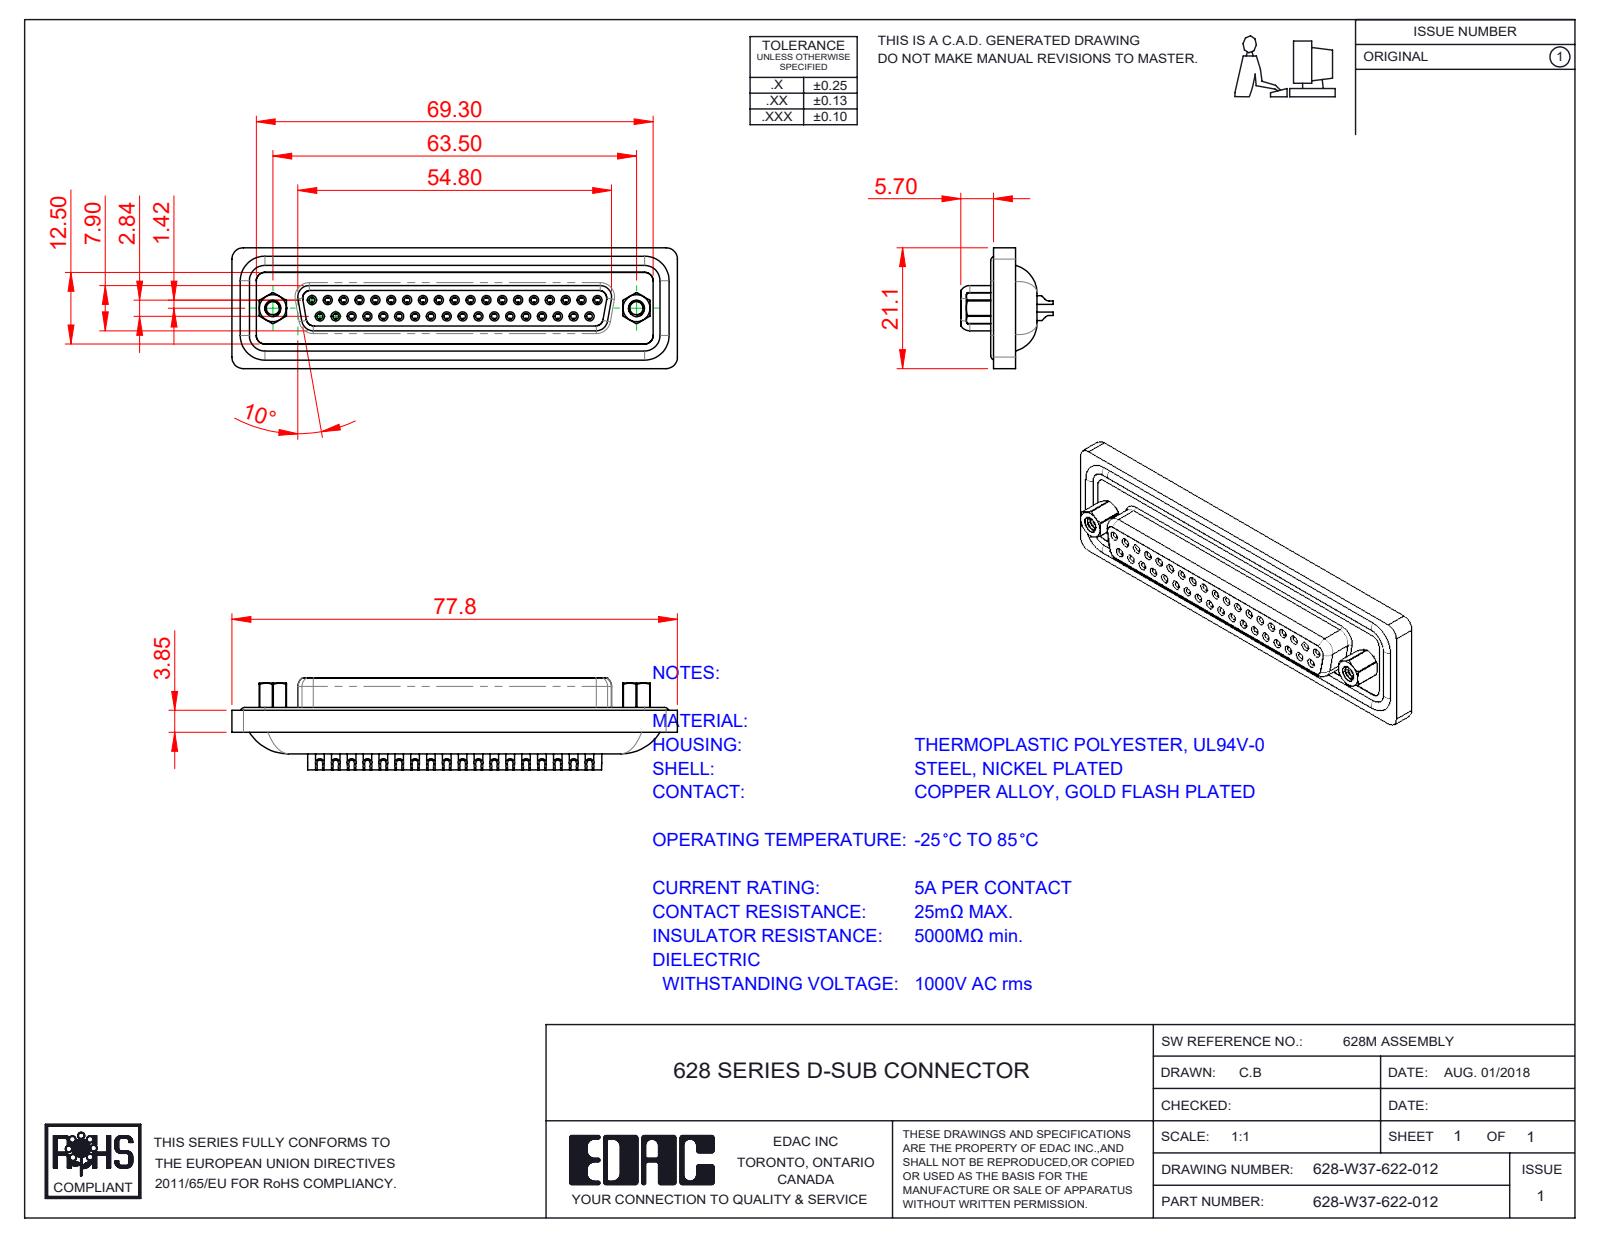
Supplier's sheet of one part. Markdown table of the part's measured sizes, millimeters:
| quantity | value |
| --- | --- |
| part name | 628W Waterproof Housing_37 Contacts; 628W Contact Row 1_22; 628W Housing_37 Contacts; 628W 4-40 Hex Standoff (+4 more) |
| STEP written by | SolidWorks 2020 (CONFIG_CONTROL_DESIGN) |
| units | millimeters |
| bodies | 45 solids, 2532 faces (730 planar, 1071 cylindrical, 731 other) |
| overall size | 77.8 × 21.1 × 16.1 |
| volume | 11 076 mm³ |
| surface area | 18 089 mm² |
| round holes (diameter × count) | 1 × 37, 1.1 × 37, 1.5 × 37, 1.7 × 37, 1.8 × 37, 2 × 37, 2.26 × 2, 2.29 × 2, 4 × 2, 4.8 × 2, 5 × 2 |
| round bosses / shafts (diameter × count) | 1.6 × 41, 2.2 × 37, 1.5 × 8, 4.9 × 2, 2.79 × 2 |
| partial cylindrical surfaces (radius × count) | 2 × 16, 1.5 × 14, 1.35 × 8, 2.7 × 6, 0.5 × 4, 0.9 × 4, 1.6 × 4, 1.75 × 4 |
| main face-to-face distances | 0.4, 7.45, 7.5, 8.45, 6.2, 13.65, 4.1, 1.1, 2.75, 8 |
| hole center spacings | 3.16, 2.77, 5.54, 8.31, 5.04, 7.49, 11.08, 13.85 |
